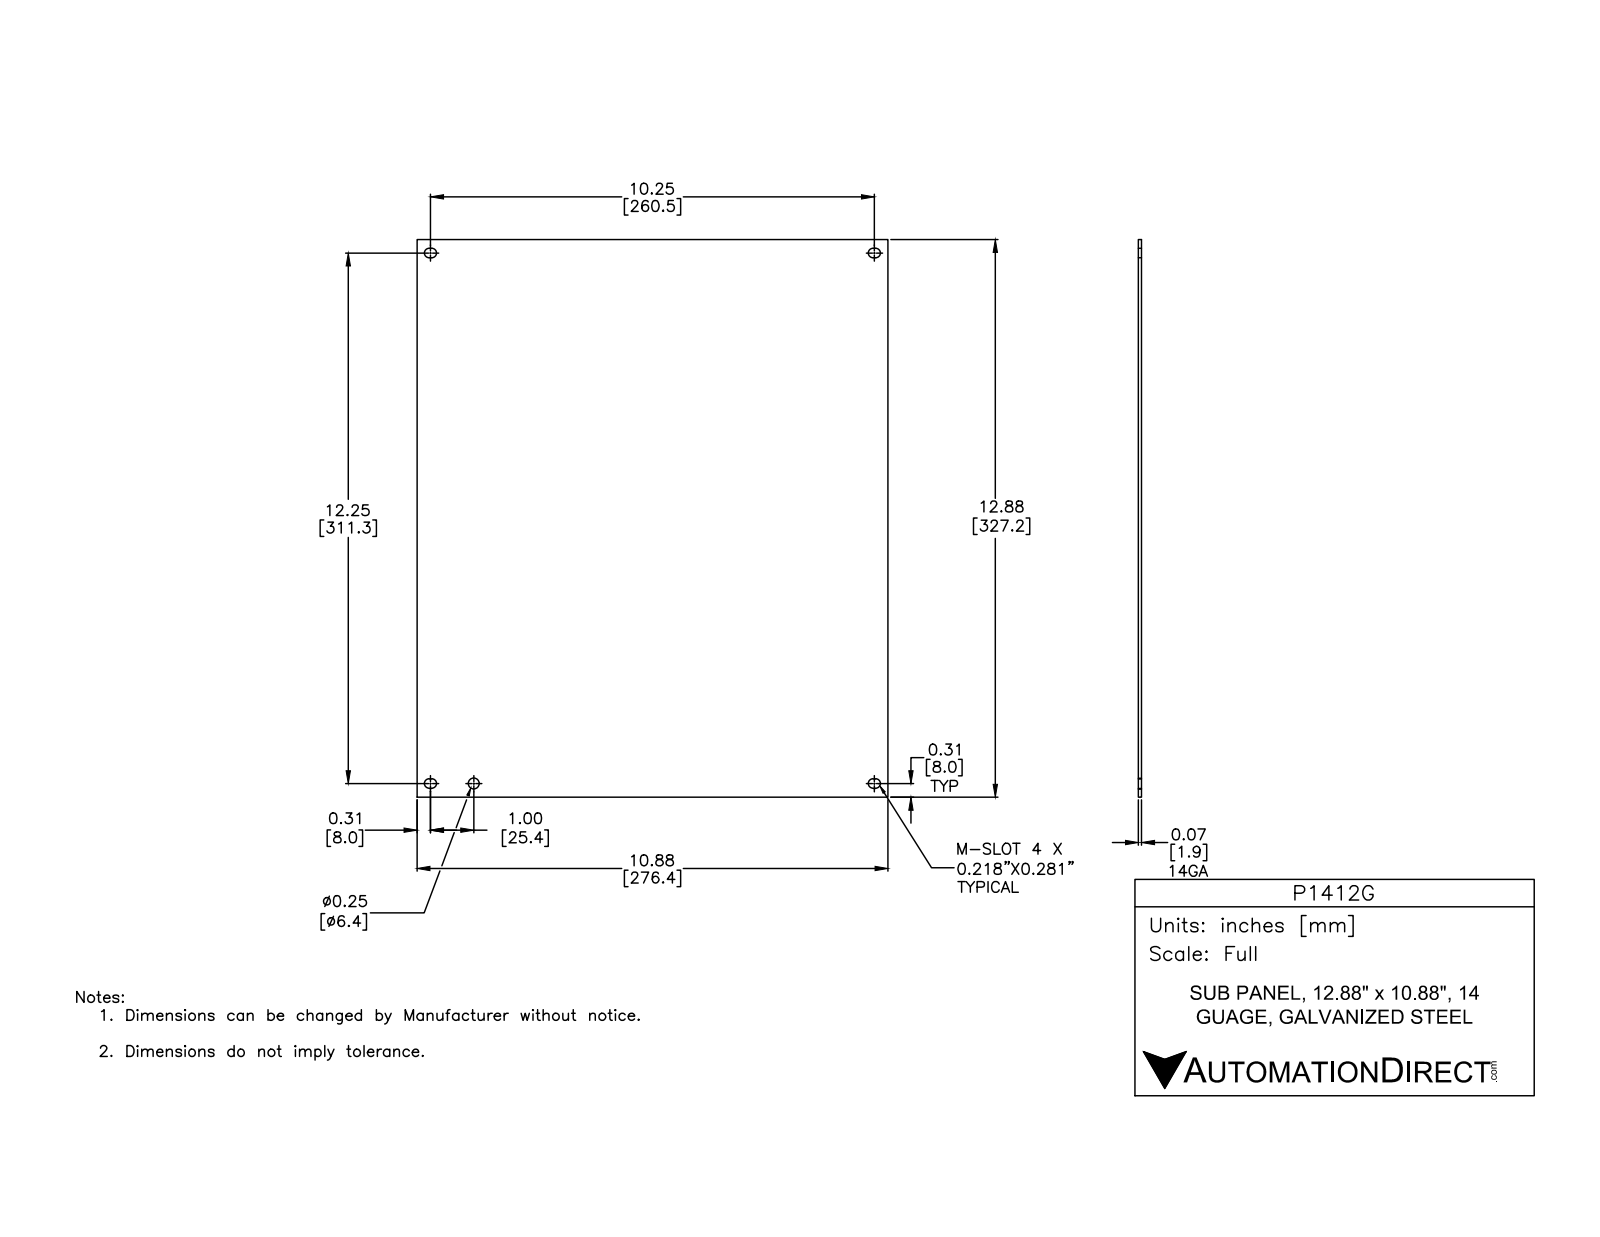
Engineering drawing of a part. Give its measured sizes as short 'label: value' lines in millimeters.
name: P1412G
written by: Autodesk Inventor 2012 (AUTOMOTIVE_DESIGN)
unit: mm
bodies: 1 solid, 23 faces (14 planar, 9 cylindrical, 0 other)
size: 327.2 × 276.4 × 1.9
volume: 169 600 mm³; area: 183 000 mm²
holes: 1× ⌀6.4
rounds: 8× R2.8
face distances: 1.9, 276.4, 327.2, 10.7, 316.4, 5.2, 322, 5.5, 311.3, 316.8
